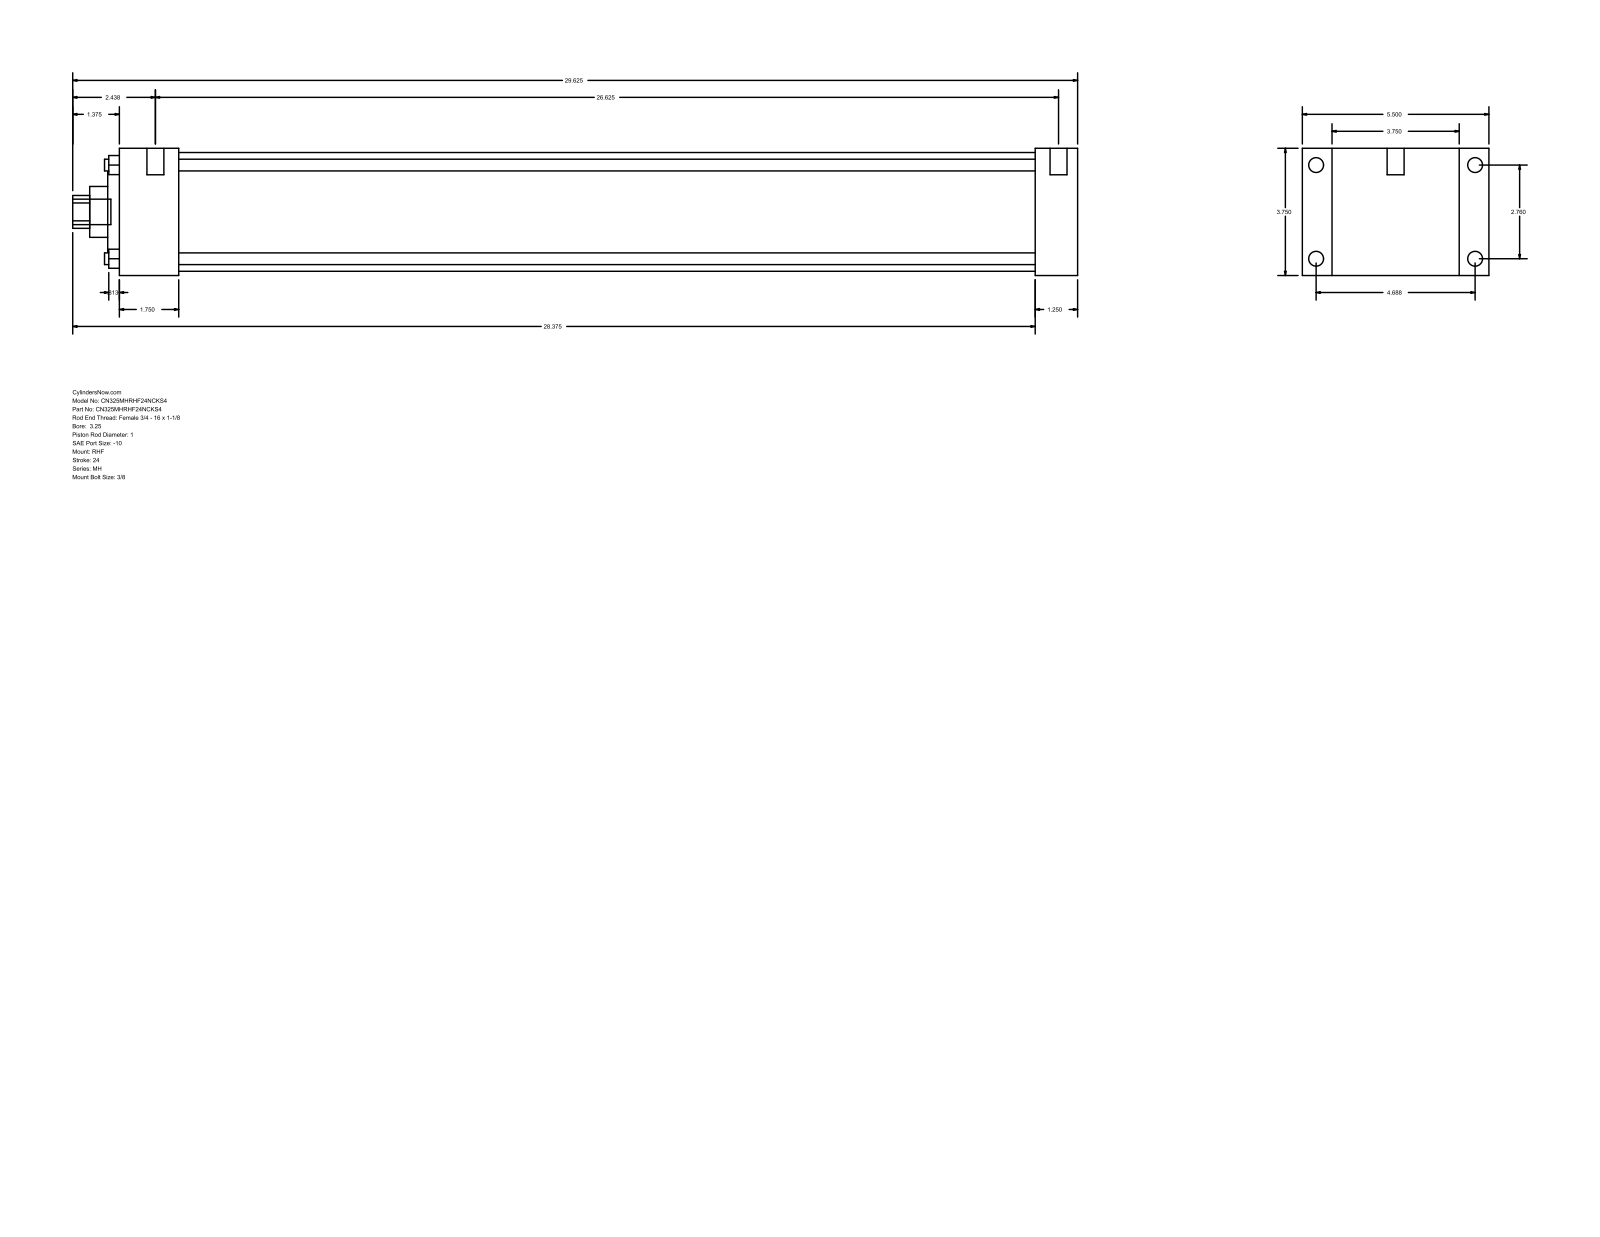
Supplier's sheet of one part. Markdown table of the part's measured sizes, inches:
| quantity | value |
| --- | --- |
| part name | MH_RHF__0325_1 |
| STEP written by | GSSL Pune (CONFIG_CONTROL_DESIGN) |
| units | inches |
| bodies | 0 solids, 90 faces (61 planar, 29 cylindrical, 0 other) |
| overall size | 29.625 × 5.5 × 3.75 |
| round holes (diameter × count) | 0.345 × 4, 1 × 1, 1.5 × 1, 2.375 × 1, 3.5 × 1 |
| round bosses / shafts (diameter × count) | 0.438 × 4, 0.219 × 4, 0.5 × 2, 0.75 × 1 |
| partial cylindrical surfaces (radius × count) | 0.484 × 1 |
| main face-to-face distances | 3.75, 1.25, 0.875, 4.625, 27, 28.25, 5.5, 1.75, 25.25, 26.5 |
| hole center spacings | 1.952, 2.76, 3.903 |
